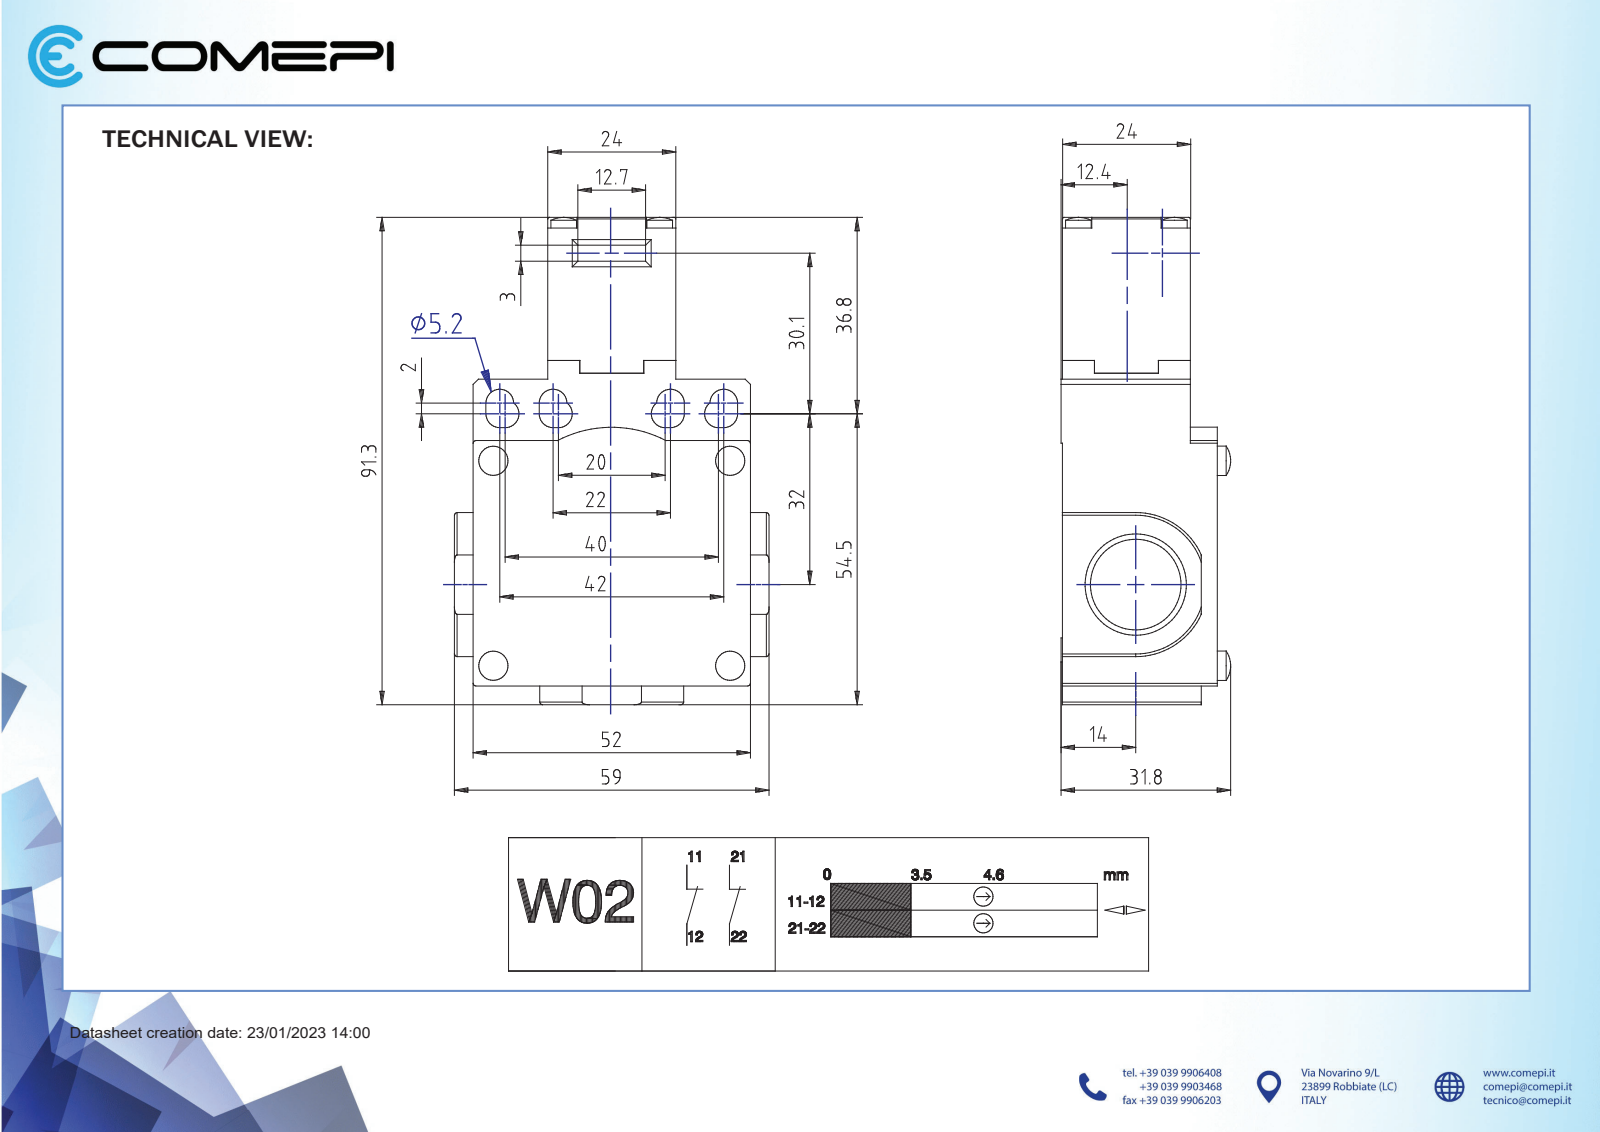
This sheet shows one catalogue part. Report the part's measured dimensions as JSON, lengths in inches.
{"part_name": "SDM2K10W02", "step_written_by": "SolidWorks 2021 (AUTOMOTIVE_DESIGN)", "units": "inches", "bodies": {"solids": 2, "faces": 181, "planar": 105, "cylindrical": 59, "other": 17}, "overall_size": [3.594, 2.323, 1.252], "volume_in3": 6.047, "surface_area_in2": 33.47, "round_holes": [[0.669, 2], [0.748, 2]], "round_bosses_or_shafts": [[0.217, 4], [0.189, 4]], "partial_cylinders_radius": [[0.102, 12], [0.02, 10], [0.012, 4], [0.098, 4], [0.531, 2], [0.394, 1], [0.4, 1], [0.866, 1]], "face_to_face_distances": [1.144, 0.945, 0.551, 1.496, 0.138, 0.199, 2.047, 2.307, 0.236, 2.185]}
